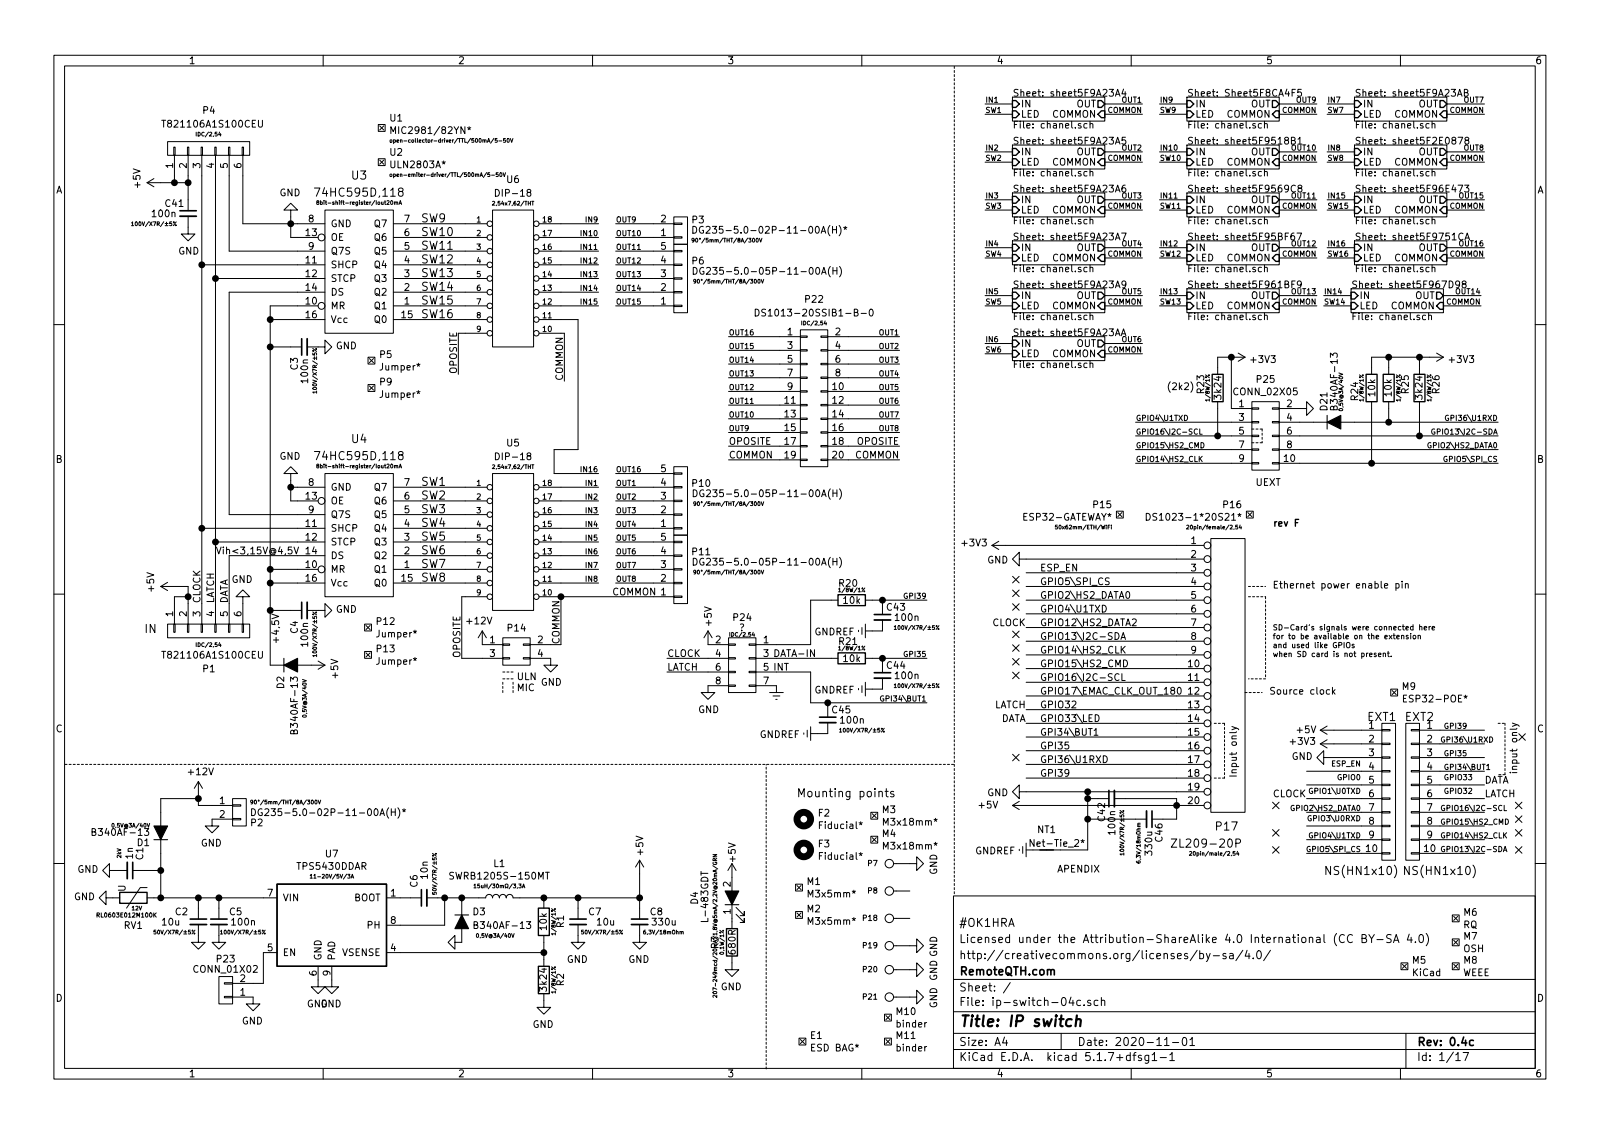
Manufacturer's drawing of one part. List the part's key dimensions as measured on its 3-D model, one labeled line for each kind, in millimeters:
Part name (STEP PRODUCT): IDC-Header_2x04_P2.54mm_Vertical; IDC-Header_2x05_P2.54mm_Vertical; CP_EIA-7343-20_Kemet-V; R_0805_2012Metric (+6 more)
STEP written by: KiCad to STEP converter (AUTOMOTIVE_DESIGN)
Units: millimetres
Bodies: 226 solids, 39756 faces (31751 planar, 7604 cylindrical, 401 other)
Overall size (bounding box): 119.2 × 90 × 26.3
Volume: 47 166 mm³ · Surface area: 70 621 mm²
Round holes (diameter × count): ⌀1 ×75, ⌀0.5 ×48, ⌀1.02 ×46, ⌀1.2 ×39, ⌀0.51 ×36, ⌀0.8 ×36, ⌀0.6 ×29, ⌀3.5 ×19, ⌀0.3 ×8, ⌀0.9 ×8, ⌀3.2 ×8, ⌀1.1 ×4
Round bosses / shafts (diameter × count): ⌀1.72 ×36, ⌀1.52 ×36, ⌀1 ×30, ⌀0.5 ×10, ⌀10 ×1
Partial cylindrical surfaces — rounded edges, fillets, slot ends (radius × count): R0.5 ×95, R0.37 ×34, R0.9 ×34, R0.38 ×23, R0.2 ×22, R0.13 ×21, R0.15 ×18, R0.3 ×17
Main face-to-face distances: 1.6, 11.85, 13.45, 10.25, 26, 5, 0.53, 9.72, 2.13, 11.32
Hole centre spacings: 7.62, 2.54, 12.7, 5.08, 8.03, 9.16, 10.16, 5
